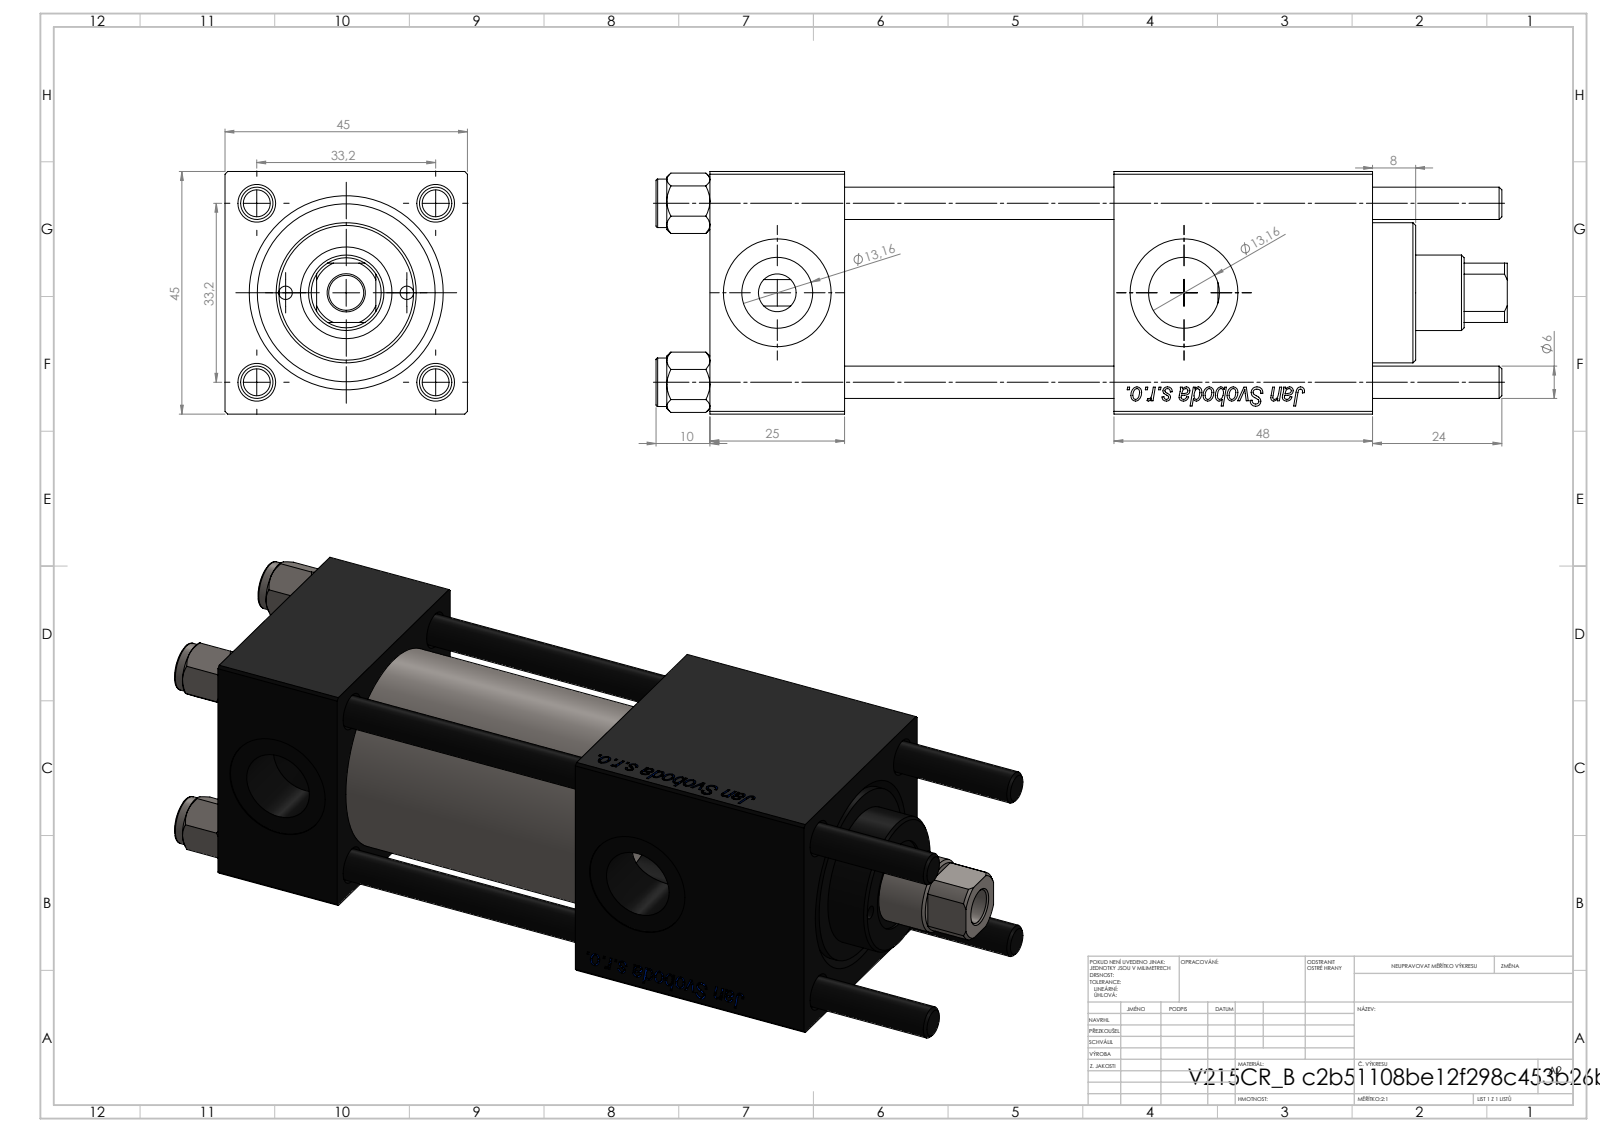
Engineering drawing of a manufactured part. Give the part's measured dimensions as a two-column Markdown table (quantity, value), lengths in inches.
| quantity | value |
| --- | --- |
| part name | V215CR_VCP_B; V215_VC_A; NUT_M5_B; V215CR_B_TYCINKA (+1 more) |
| STEP written by | SolidWorks 2019 (CONFIG_CONTROL_DESIGN) |
| units | inches |
| bodies | 11 solids, 1163 faces (433 planar, 82 cylindrical, 648 other) |
| overall size | 6.22 × 1.772 × 1.772 |
| volume | 12.1 in³ |
| surface area | 112.8 in² |
| round holes (diameter × count) | 0.236 × 4, 0.098 × 2, 0.276 × 2, 0.518 × 2, 0.787 × 2, 0.256 × 1, 0.551 × 1, 0.669 × 1, 0.945 × 1, 1.26 × 1, 1.299 × 1 |
| round bosses / shafts (diameter × count) | 0.354 × 4, 1.496 × 1, 1.024 × 1 |
| partial cylindrical surfaces (radius × count) | 0.256 × 1 |
| main face-to-face distances | 1.772, 0.984, 4.843, 3.858, 1.969, 2.953, 1.89, 3.713, 2.728, 0.76 |
| hole center spacings | 0.687, 0.924, 1.276, 1.307, 0.443, 1.848, 0.886, 2.972 |
